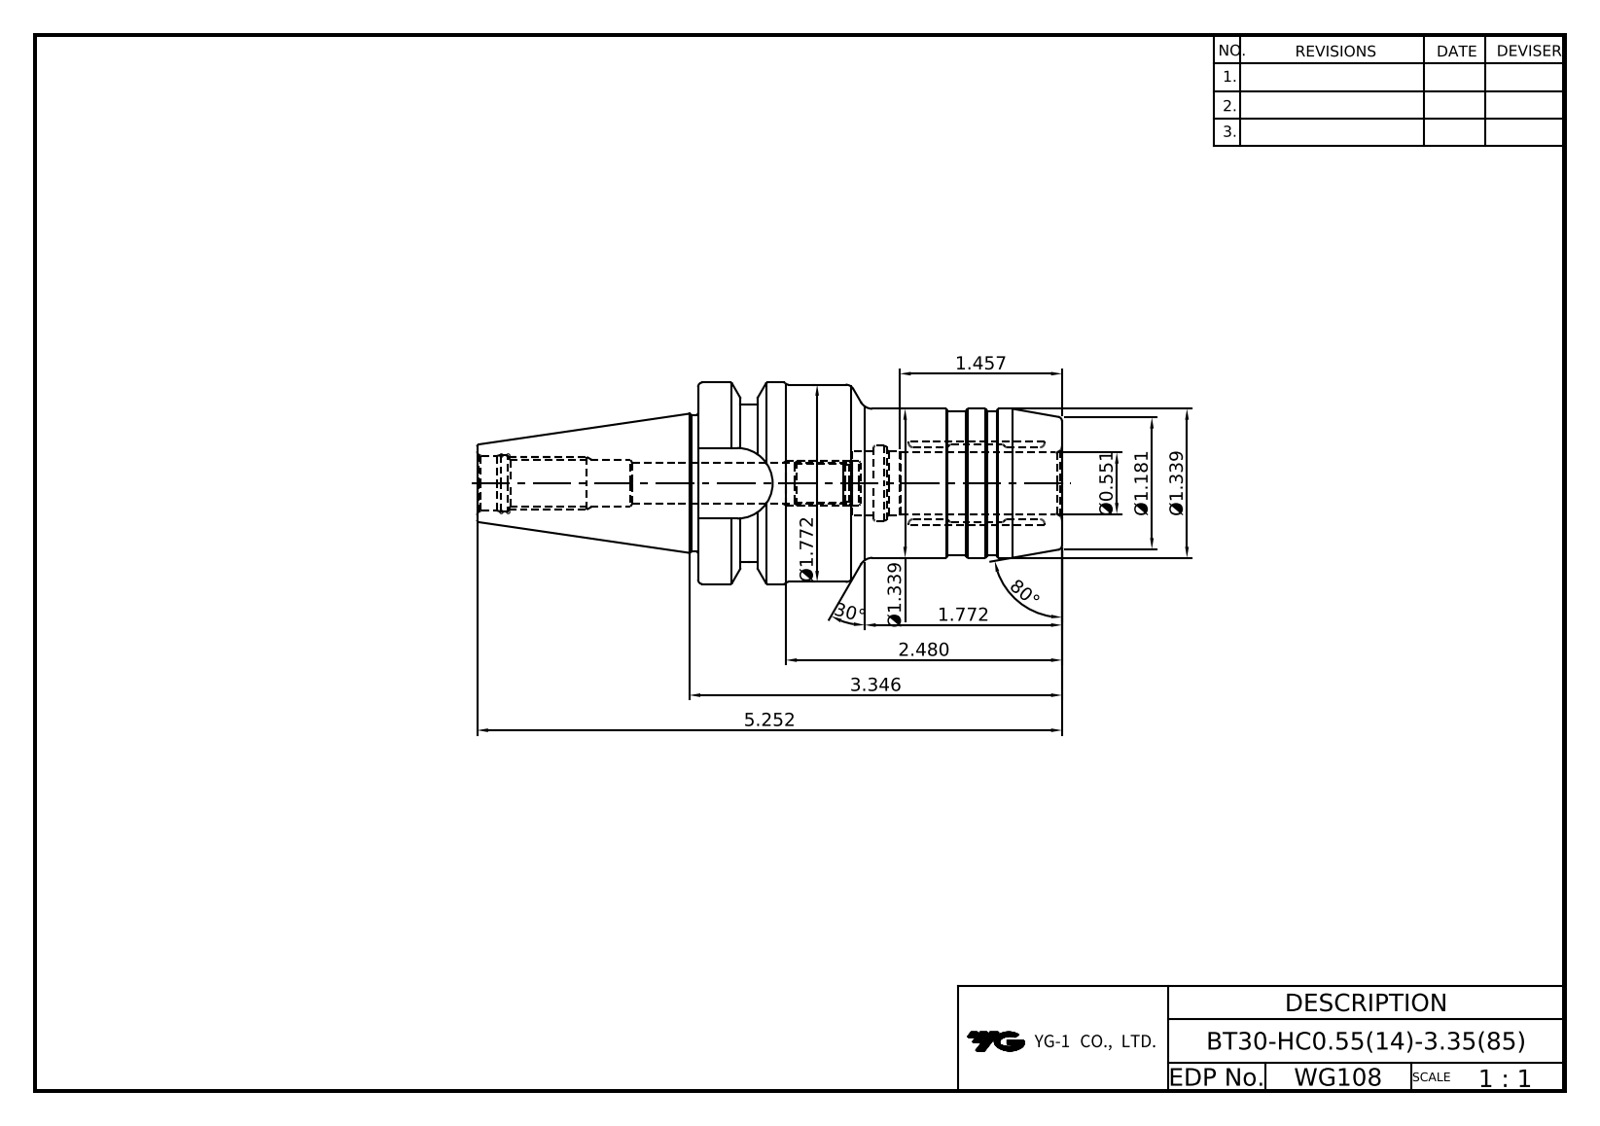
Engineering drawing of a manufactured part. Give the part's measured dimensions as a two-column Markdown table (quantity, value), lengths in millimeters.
| quantity | value |
| --- | --- |
| part name | LO-BT30ADB-HC14-85 |
| STEP written by | Autodesk Inventor 2022 (AUTOMOTIVE_DESIGN) |
| units | millimeters |
| bodies | 1 solid, 93 faces (20 planar, 38 cylindrical, 35 other) |
| overall size | 133.4 × 46 × 46 |
| volume | 104 839 mm³ |
| surface area | 22 075 mm² |
| round holes (diameter × count) | 3.24 × 4, 4 × 4, 8.92 × 1, 10.11 × 1, 12.5 × 1, 13.1 × 1, 14 × 1, 14.6 × 1 |
| round bosses / shafts (diameter × count) | 46 × 1, 44.5 × 1, 34 × 1, 33 × 1, 31.2 × 1 |
| partial cylindrical surfaces (radius × count) | 8.05 × 1, 18 × 1 |
| main face-to-face distances | 83, 32.6, 13.6, 69.4, 9.6, 4, 73.4, 35, 25.4, 21.4 |
